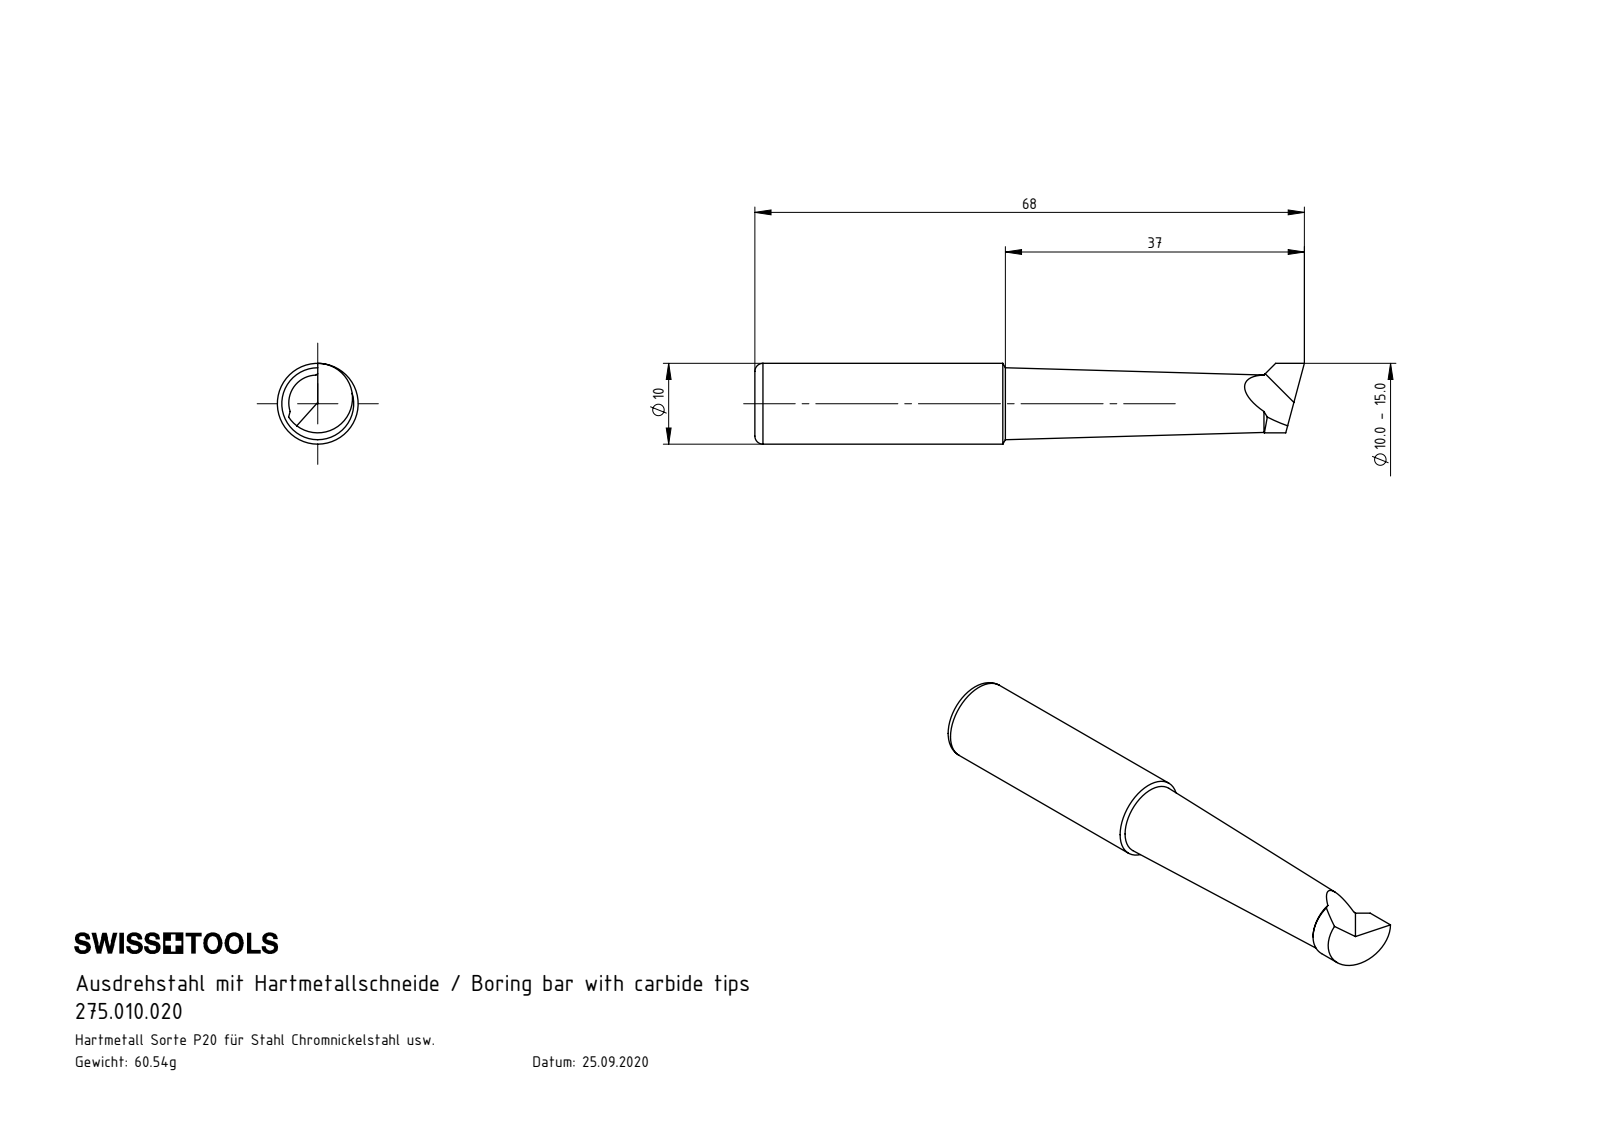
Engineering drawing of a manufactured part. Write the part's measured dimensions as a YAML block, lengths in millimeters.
part_name: "275.010.020"
step_written_by: "SolidWorks 2022 (CONFIG_CONTROL_DESIGN)"
units: millimeters
bodies: {solids: 1, faces: 16, planar: 4, cylindrical: 3, other: 9}
overall_size: [68, 10, 10]
volume: 4175
surface_area: 1987
round_bosses_or_shafts:
  - {diameter: 10, count: 1}
partial_cylinders:
  - {radius: 4.3, count: 1}
